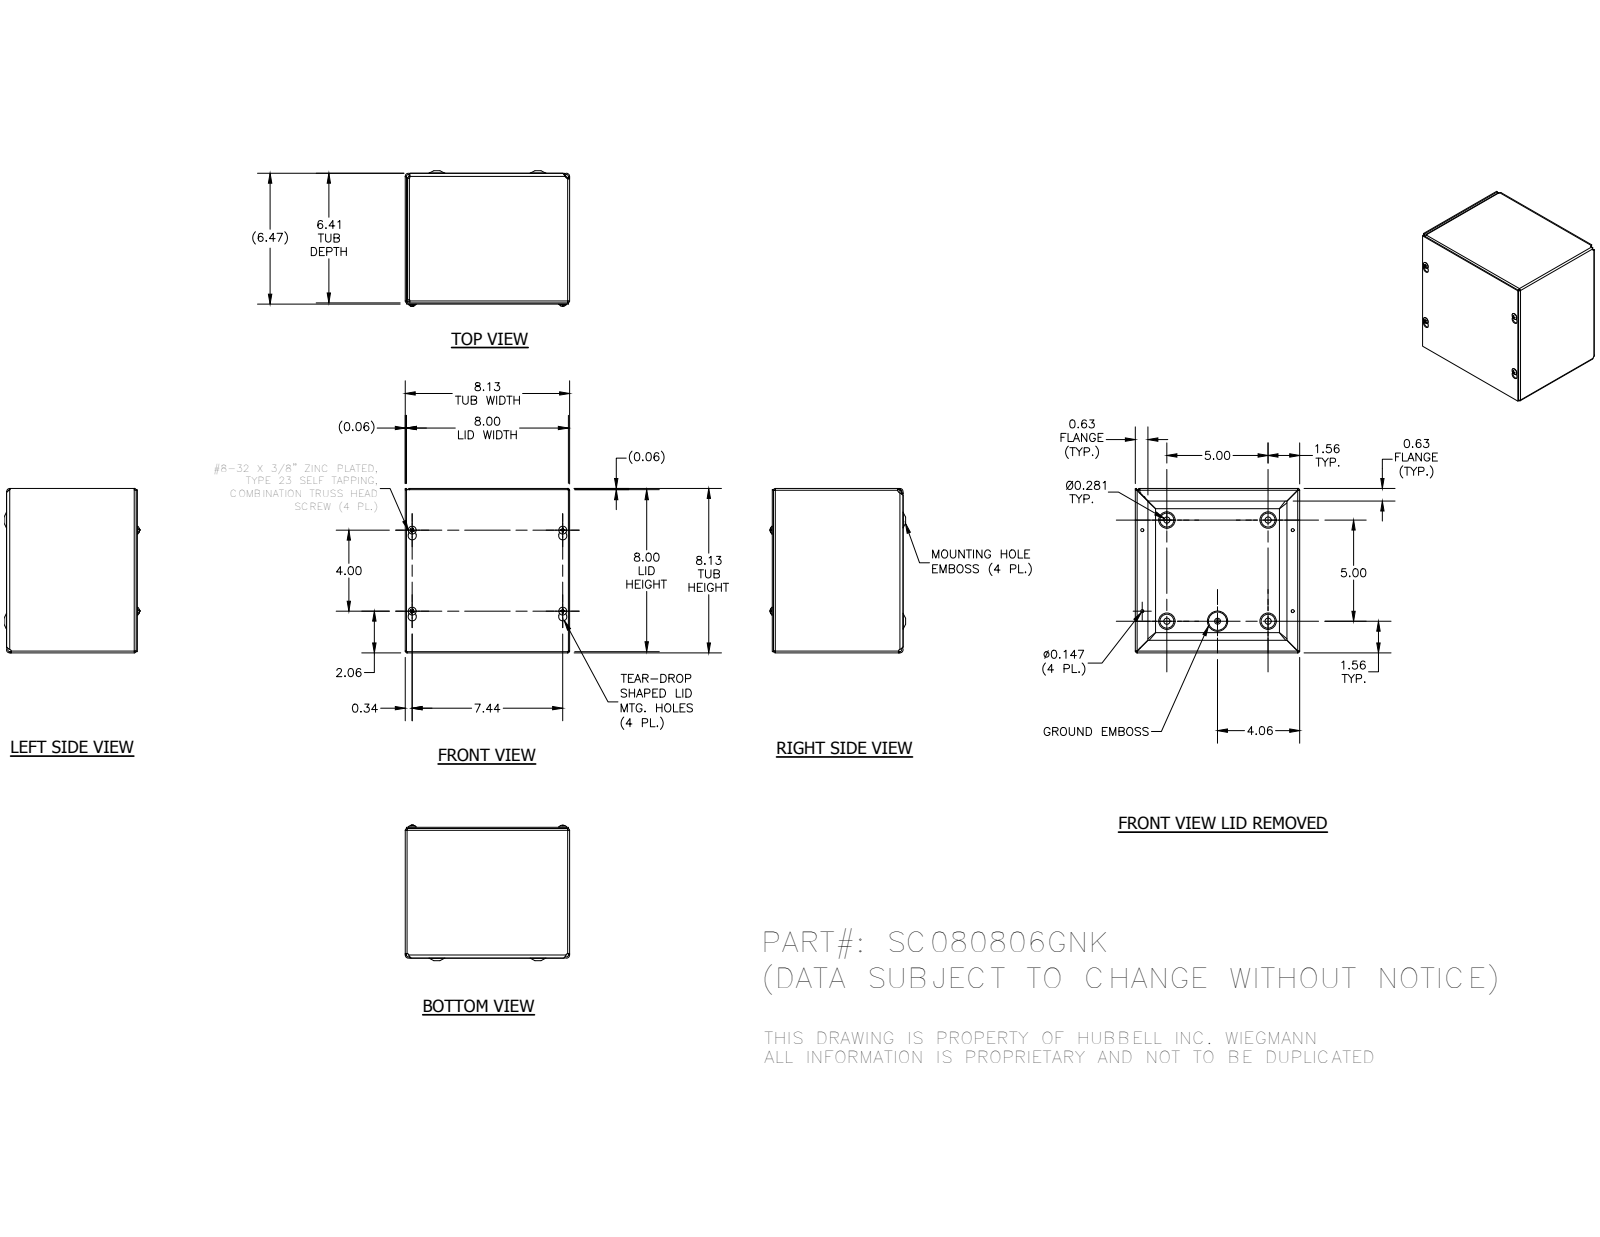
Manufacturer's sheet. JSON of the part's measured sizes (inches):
{"part_name": "SC0808GNKBKP; SC080806GNKWRA; SC0808GNKLID; 34056 (+1 more)", "step_written_by": "Autodesk Inventor 2014 (AUTOMOTIVE_DESIGN)", "units": "inches", "bodies": {"solids": 7, "faces": 358, "planar": 133, "cylindrical": 73, "other": 152}, "overall_size": [8.125, 8.125, 6.693], "volume_in3": 23.08, "surface_area_in2": 754.4, "round_holes": [[0.147, 4], [0.3, 4], [0.165, 1]], "round_bosses_or_shafts": [[0.384, 4], [0.164, 4], [0.228, 1]], "partial_cylinders_radius": [[0.031, 8], [0.093, 8], [0.055, 4], [0.062, 4], [0.094, 4], [0.117, 4], [0.124, 4], [0.125, 4]], "face_to_face_distances": [0.062, 0.062, 8.063, 8.001, 8.125, 8.063, 6.343, 6.405, 0.063, 6.406], "hole_center_spacings": [5, 1.317, 2.5, 4, 4.661, 4.663, 5.59, 6.239]}
